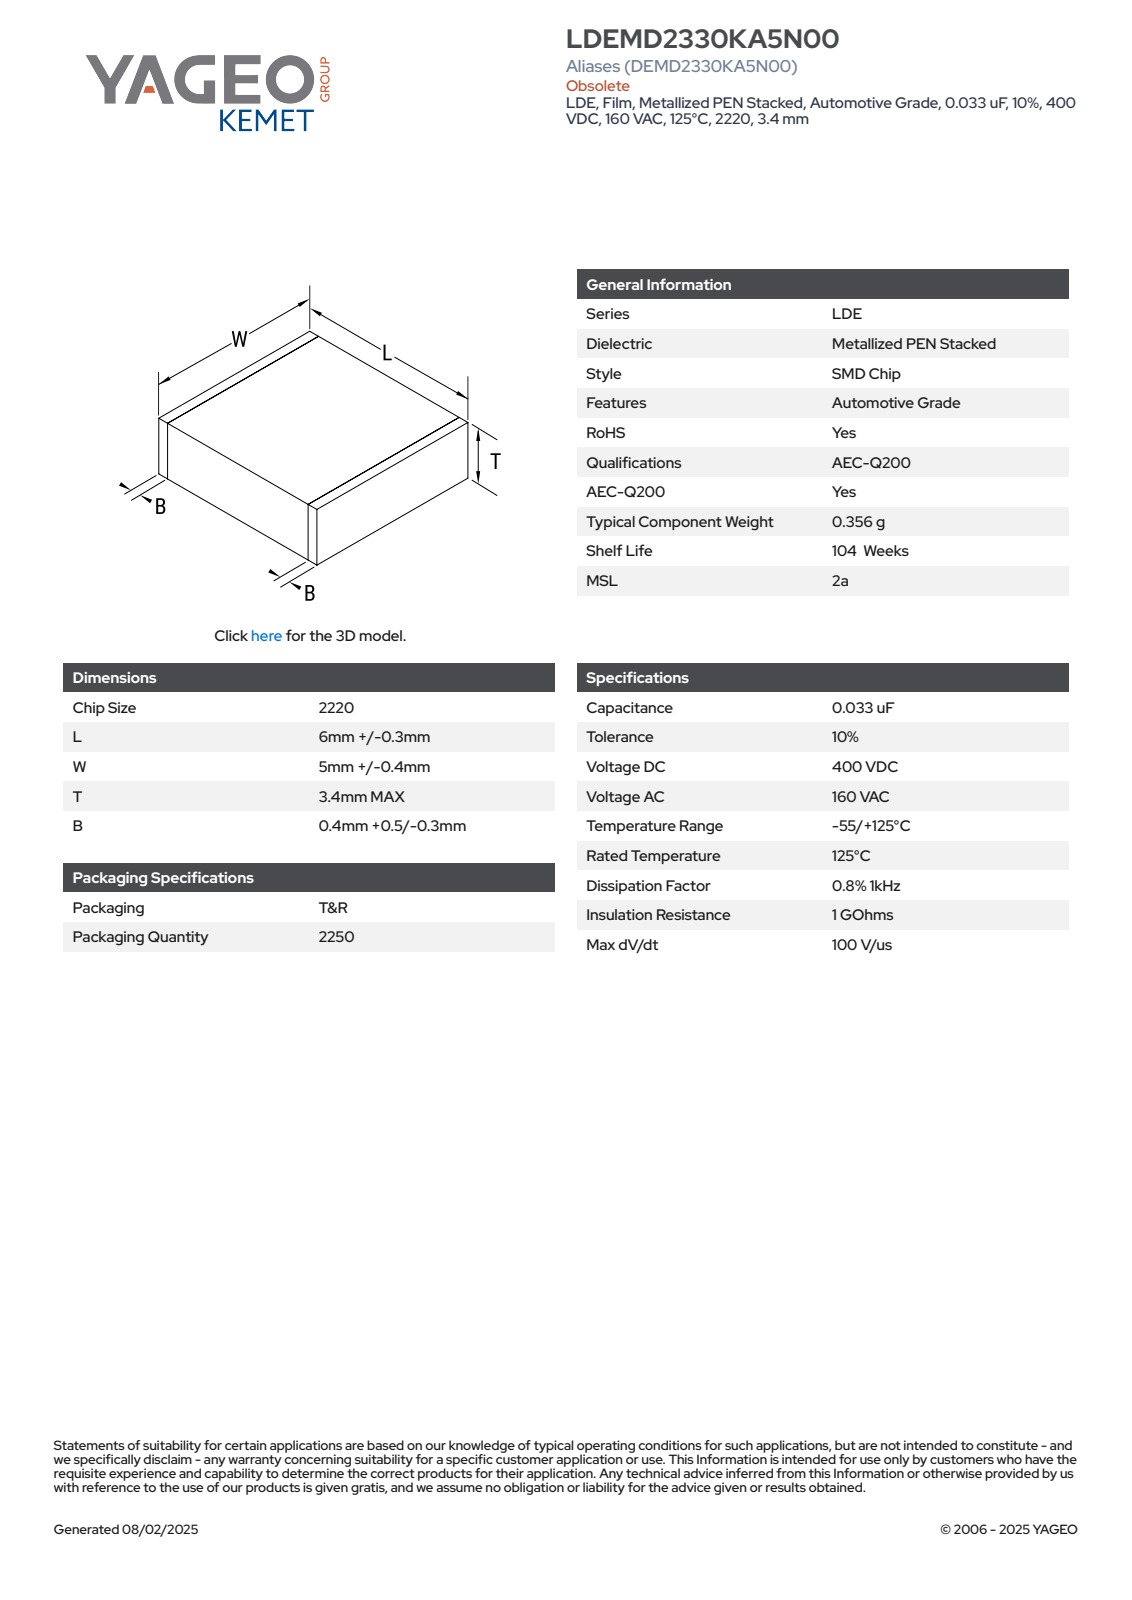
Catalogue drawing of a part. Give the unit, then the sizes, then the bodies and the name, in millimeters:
Units: millimetres
Overall size (bounding box): 6.3 × 5.4 × 3.4
Main face-to-face distances: 3.38, 6.3, 5.38, 3.39, 5.39, 3.4, 5.4, 0.5, 5.8, 5.3
Volume: 115 mm³ · Surface area: 149 mm²
Bodies: 4 solids, 73 faces (73 planar, 0 cylindrical, 0 other)
Part name (STEP PRODUCT): CFS_LDELDB_2220_L6.3W5.4T3.4B0.9
STEP written by: SolidWorks 2020 (AUTOMOTIVE_DESIGN)
